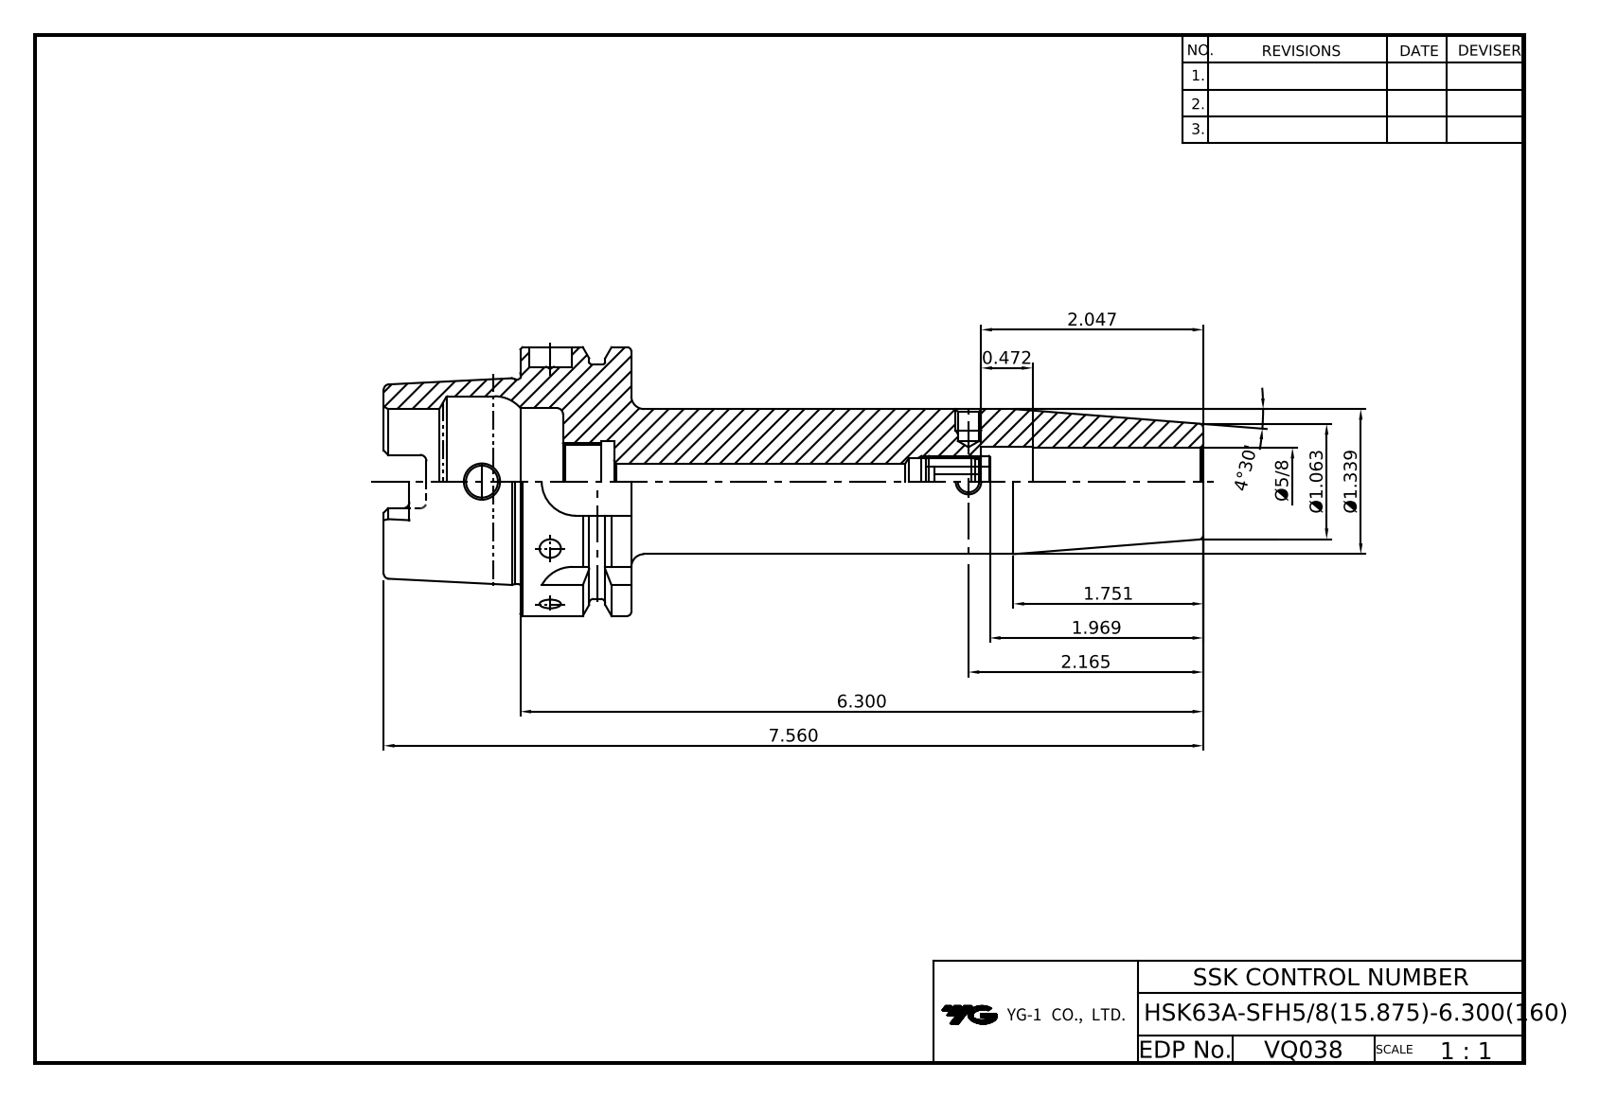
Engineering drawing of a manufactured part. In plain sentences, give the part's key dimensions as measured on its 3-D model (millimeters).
The part is named "LO-HSK63A-SFH15.875-160". Its 3-D file was written by "Autodesk Inventor 2022 (AUTOMOTIVE_DESIGN)". It is 1 solid with 116 faces: 42 planar, 34 cylindrical and 40 other. Overall it measures 192 by 63 by 63 millimeters. Its volume is 179 783 cubic millimeters and its surface area 40 577 square millimeters. Round holes: 1 of diameter 7.5, 1 of diameter 8, 1 of diameter 10, 1 of diameter 10.92, 1 of diameter 15.88, 1 of diameter 16.92, 1 of diameter 17.07, 1 of diameter 19, 1 of diameter 34, 1 of diameter 40. Round bosses or shafts: 1 of diameter 63, 1 of diameter 55, 1 of diameter 48.04. Partial cylindrical surfaces (rounded edges, fillets, slot ends): 6 of radius 1.5, 4 of radius 2.88, 4 of radius 8. The main face-to-face distances are 26, 10, 16, 32, 42, 58, 134, 12, 53, 22.
